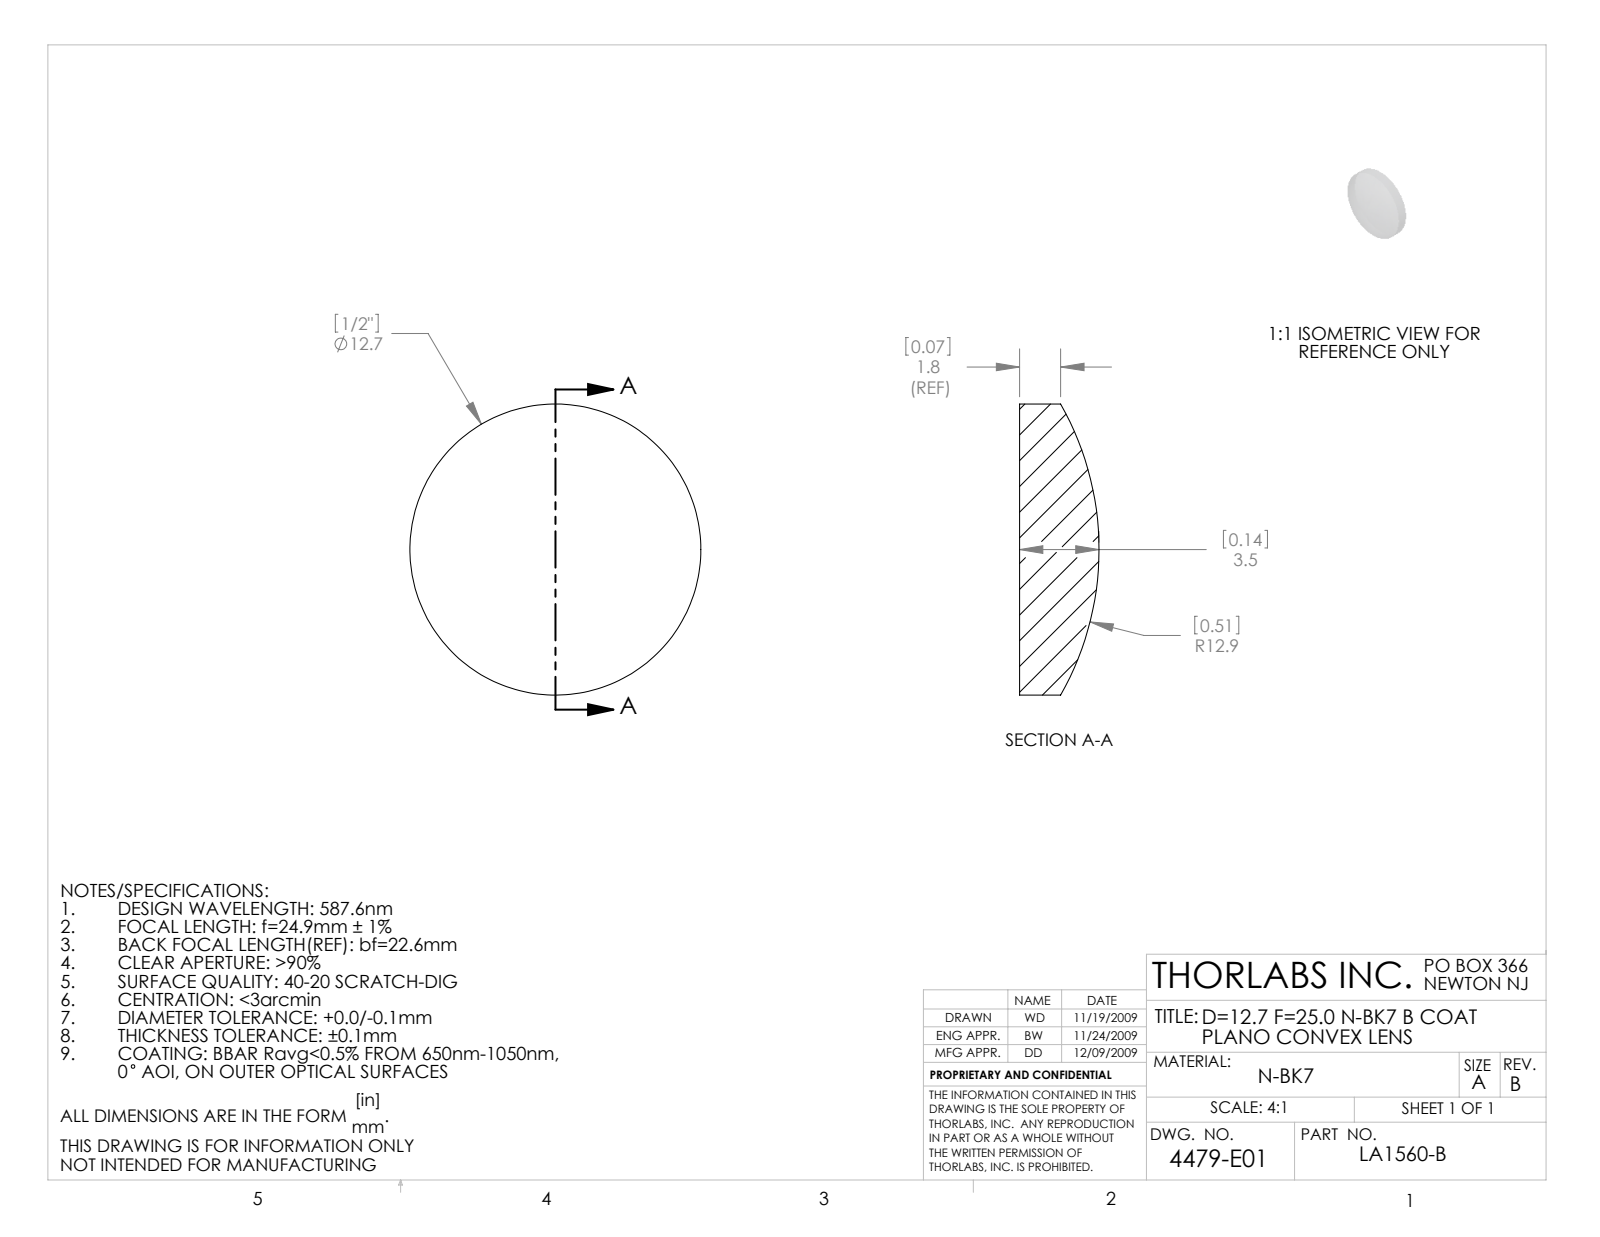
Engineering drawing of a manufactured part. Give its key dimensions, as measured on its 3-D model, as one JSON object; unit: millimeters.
{"part_name": "4479-E0W", "step_written_by": "SolidWorks 2009 (AUTOMOTIVE_DESIGN)", "units": "millimeters", "bodies": {"solids": 1, "faces": 5, "planar": 1, "cylindrical": 2, "other": 2}, "overall_size": [12.7, 12.7, 3.47], "volume_mm3": 336, "surface_area_mm2": 334, "round_bosses_or_shafts": [[12.7, 1]]}
